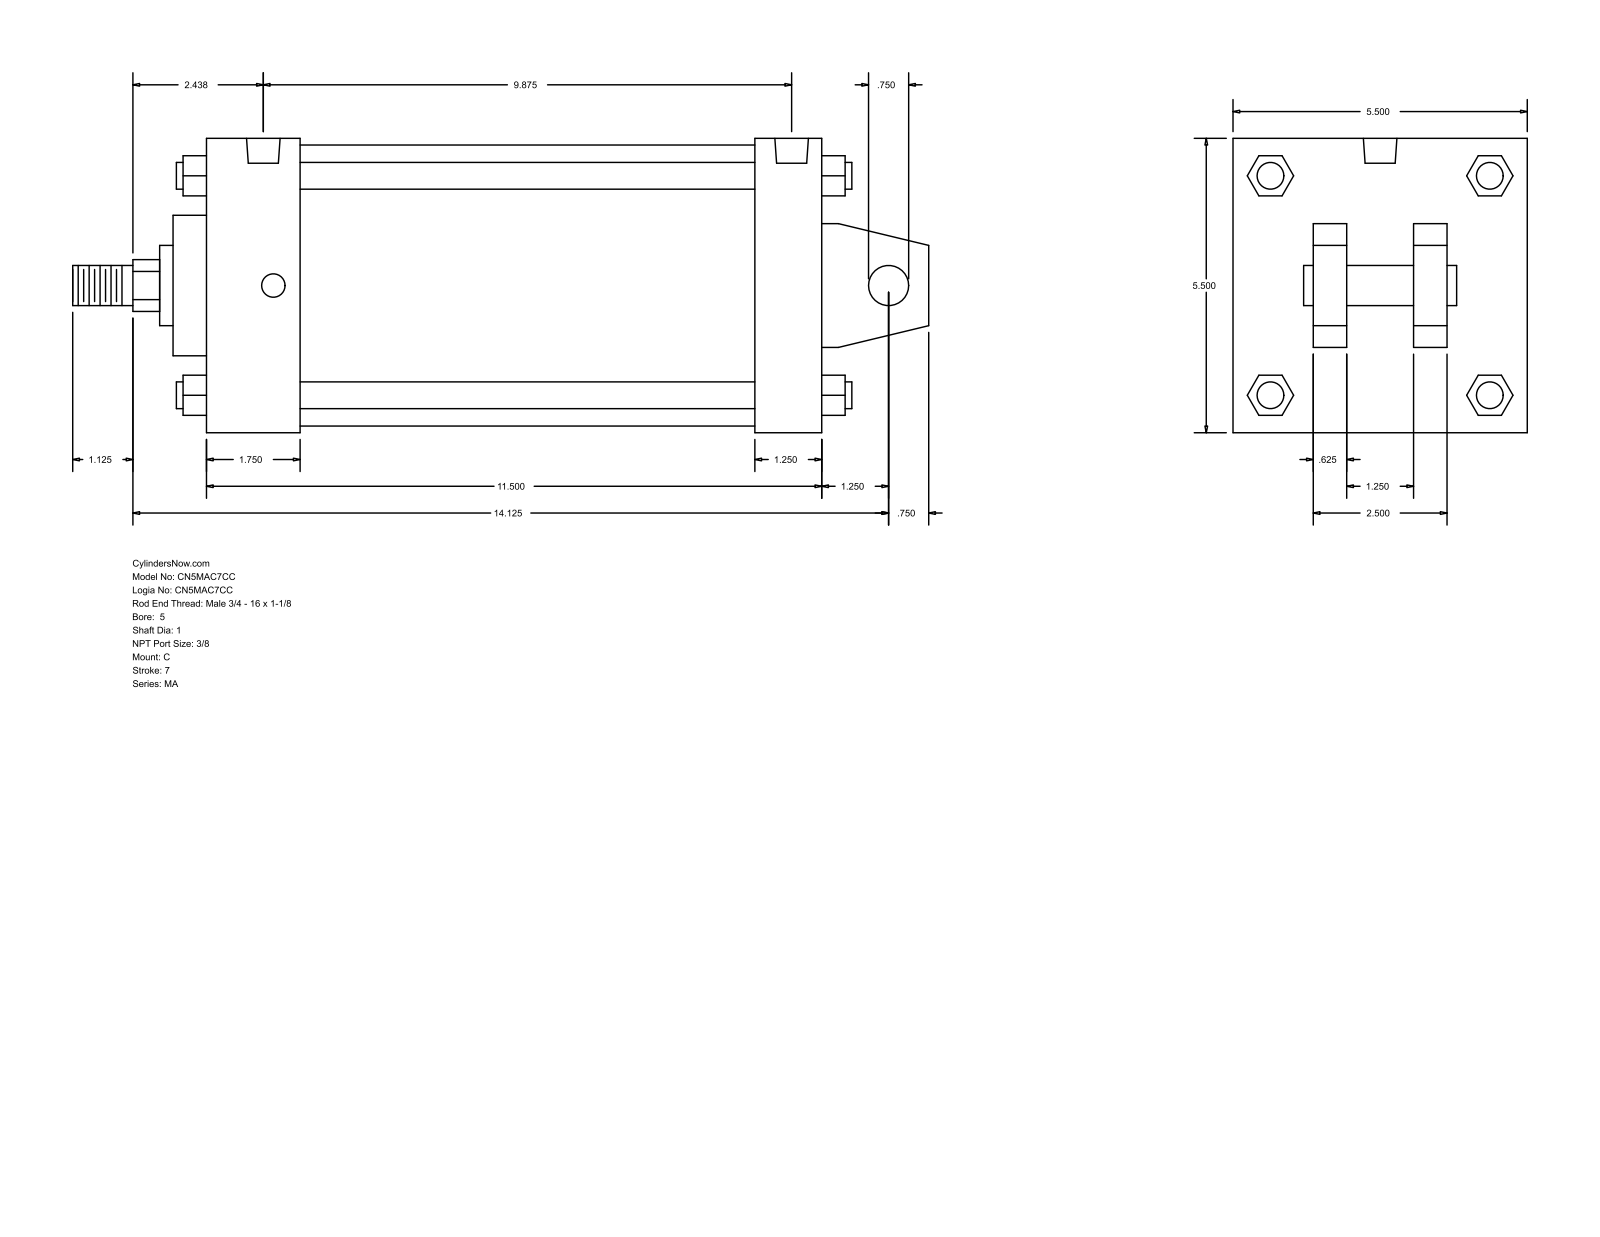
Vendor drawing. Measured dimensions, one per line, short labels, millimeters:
name: MA_C__0500_1
written by: GSSL Pune (CONFIG_CONTROL_DESIGN)
unit: mm
bodies: 0 solids, 141 faces (109 planar, 32 cylindrical, 0 other)
size: 406.4 × 139.7 × 139.7
holes: 4× ⌀11.11, 2× ⌀15.93
bosses: 4× ⌀12.7, 2× ⌀19.05, 1× ⌀133.35, 1× ⌀66.67, 1× ⌀38.1, 1× ⌀25.4
rounds: 1× R12.29
face distances: 139.7, 292.1, 15.87, 260.35, 31.75, 44.46, 215.89, 247.64, 38.1, 101.6
hole spacings: 4.76, 241.31, 246.07, 250.83
